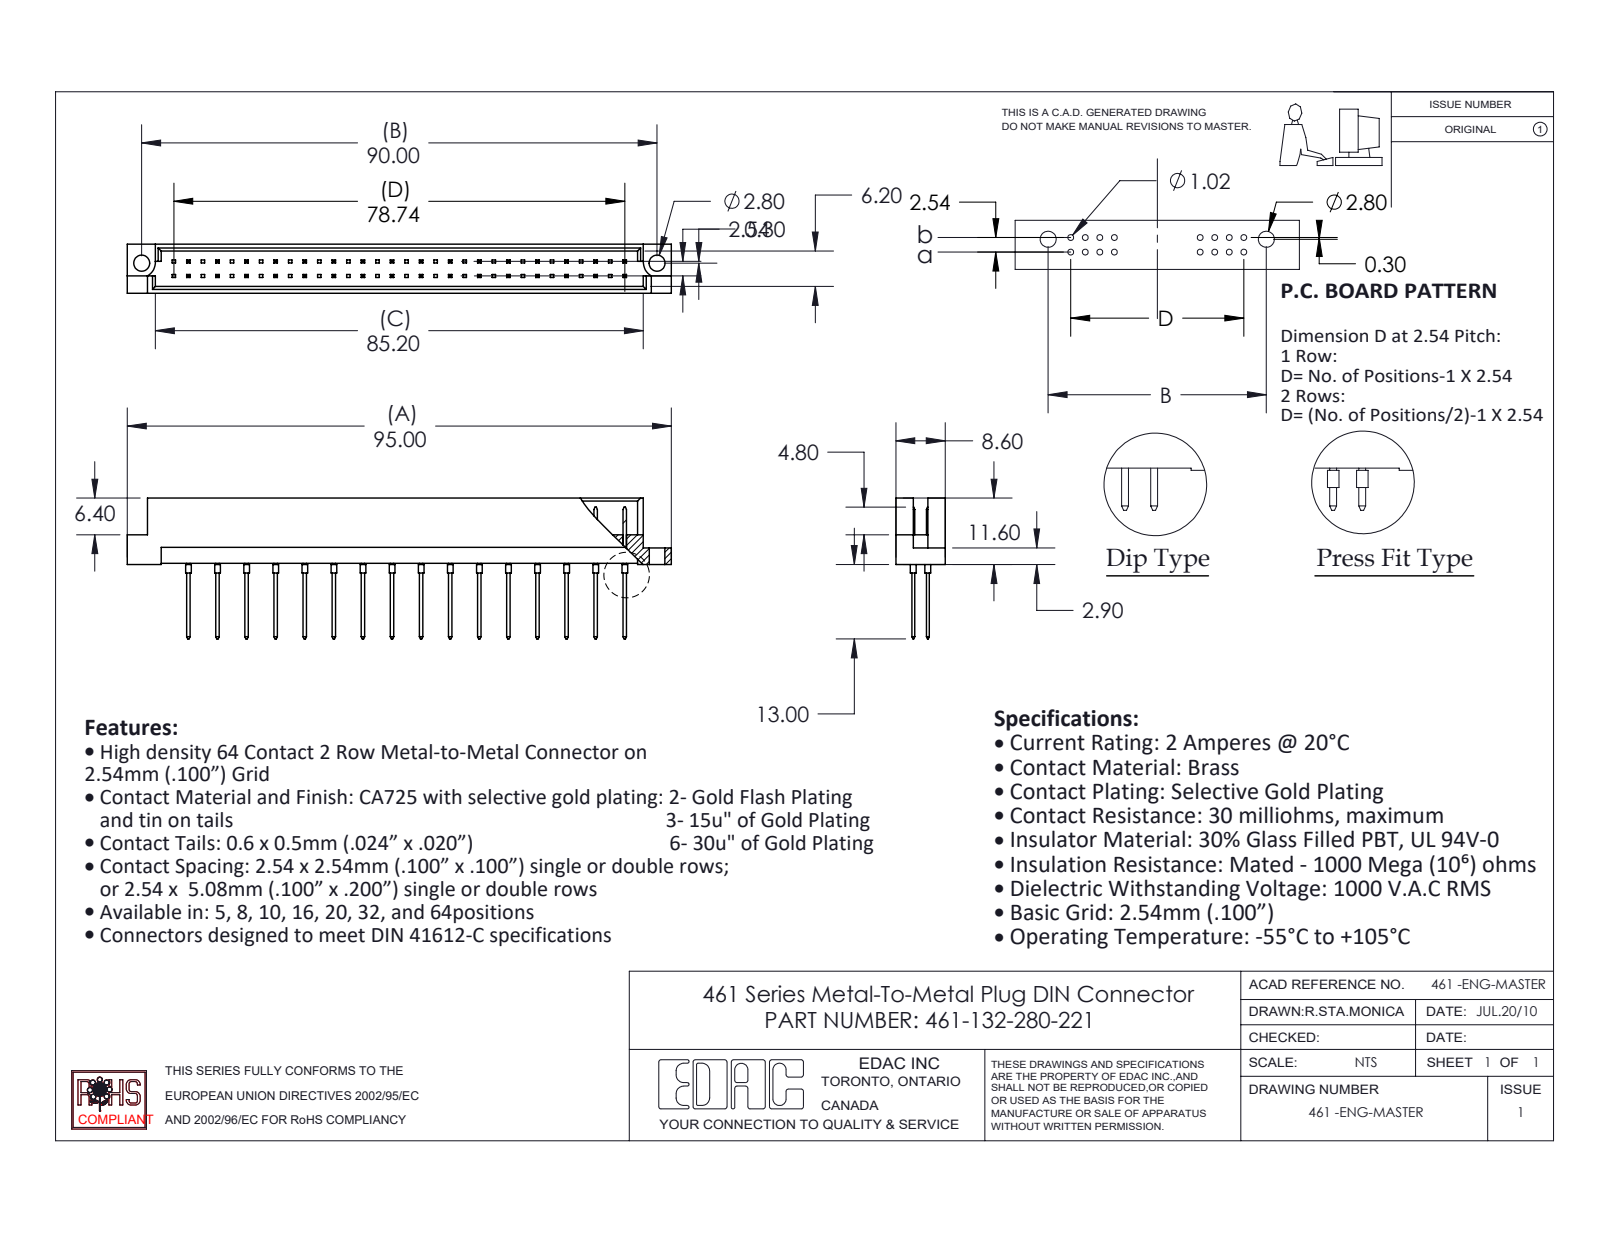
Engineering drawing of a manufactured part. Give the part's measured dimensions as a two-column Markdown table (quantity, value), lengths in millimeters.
| quantity | value |
| --- | --- |
| part name | 461-290_80; 461-132-280-221; 461 Part_64 |
| STEP written by | SolidWorks 2020 (CONFIG_CONTROL_DESIGN) |
| units | millimeters |
| bodies | 33 solids, 1009 faces (938 planar, 71 cylindrical, 0 other) |
| overall size | 95 × 24.6 × 8.6 |
| volume | 4 897 mm³ |
| surface area | 7 355 mm² |
| round holes (diameter × count) | 2.8 × 2 |
| round bosses / shafts (diameter × count) | 1 × 32 |
| partial cylindrical surfaces (radius × count) | 2.8 × 2 |
| main face-to-face distances | 1.2, 7.4, 8.6, 6.2, 2.54, 3.28, 5.32, 2.08, 4.12, 2.78 |
| hole center spacings | 90 |
